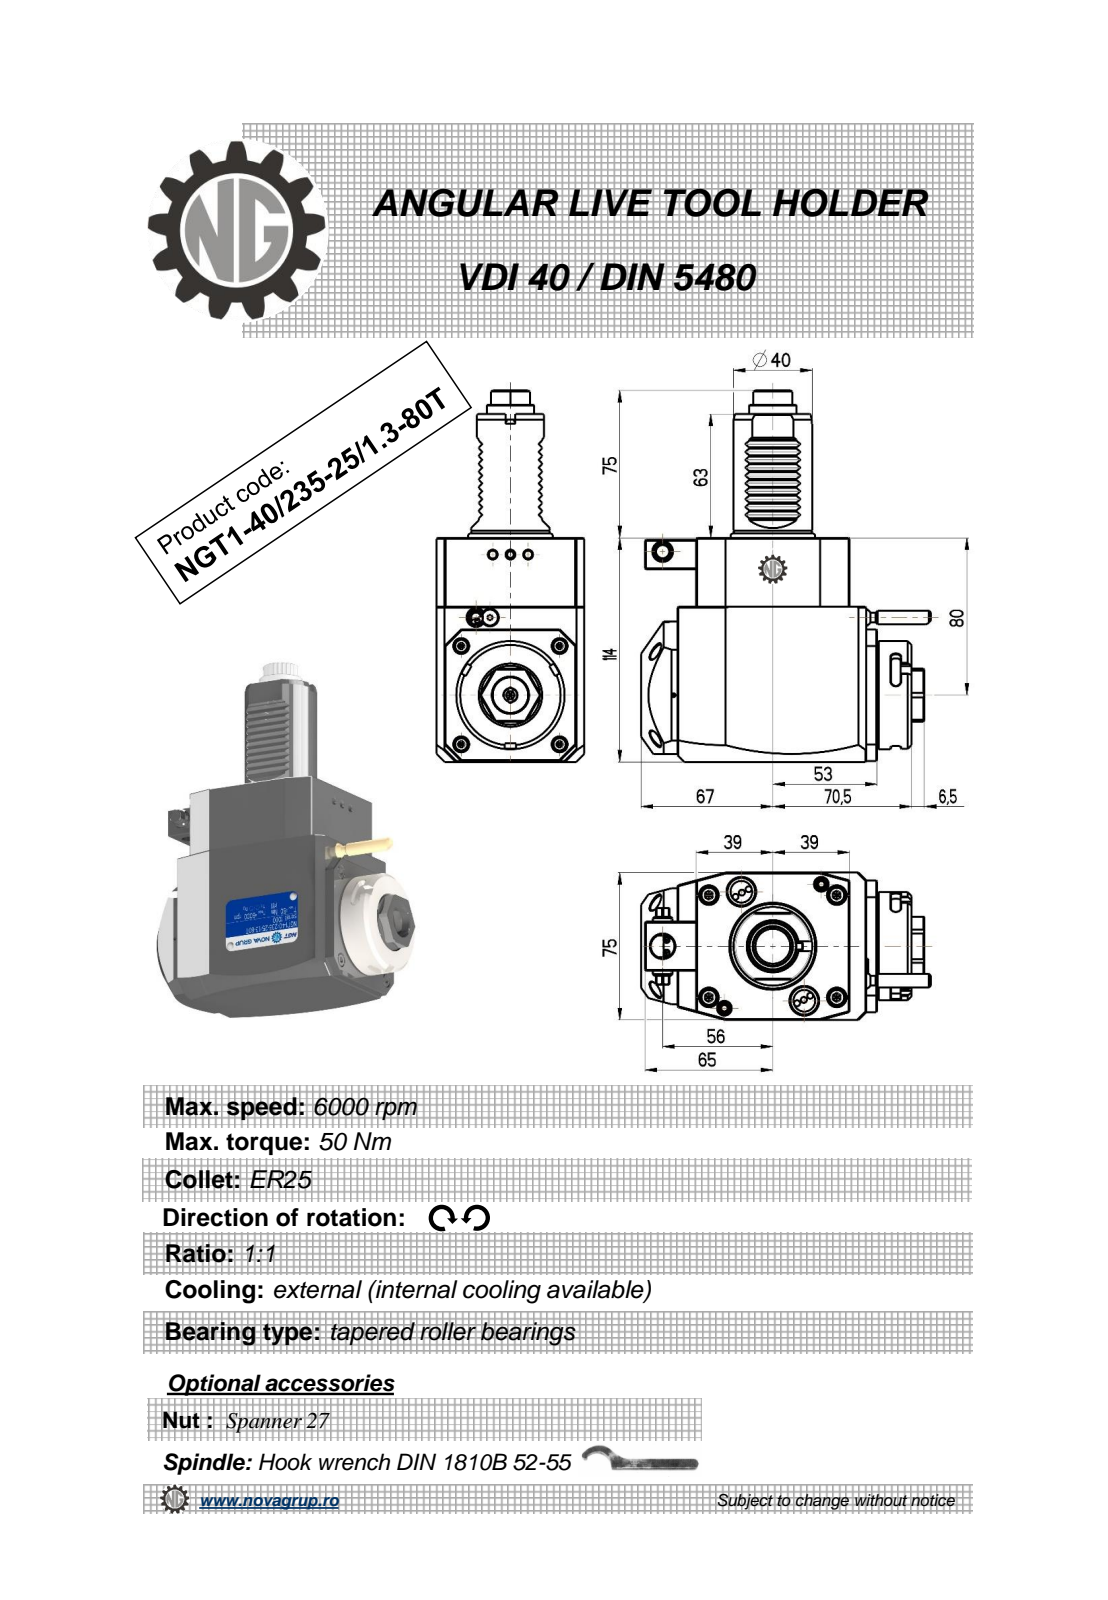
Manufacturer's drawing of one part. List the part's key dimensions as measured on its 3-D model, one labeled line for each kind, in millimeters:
Part name (STEP PRODUCT): NGT1_40_235_25_1_3_80T
STEP written by: PRO/ENGINEER BY PARAMETRIC TECHNOLOGY CORPORATION, 2010280 (CONFIG_CONTROL_DESIGN)
Units: millimetres
Bodies: 1 solid, 508 faces (222 planar, 188 cylindrical, 98 other)
Overall size (bounding box): 189 × 147.33 × 75
Volume: 955 538 mm³ · Surface area: 71 405 mm²
Round holes (diameter × count): ⌀2.5 ×1, ⌀3 ×1, ⌀9.5 ×1, ⌀12 ×1, ⌀18 ×1
Round bosses / shafts (diameter × count): ⌀8 ×2, ⌀55 ×1, ⌀48 ×1, ⌀40 ×1, ⌀24 ×1, ⌀10 ×1, ⌀7 ×1, ⌀5 ×1
Partial cylindrical surfaces — rounded edges, fillets, slot ends (radius × count): R2.08 ×48, R0.3 ×20, R2.5 ×6, R15 ×2, R180 ×2, R3.85 ×1, R4.25 ×1, R9.08 ×1
Main face-to-face distances: 75, 114, 14, 17.5, 109.5, 78, 92, 31.5, 79, 28
Hole centre spacings: 36.47, 43.2, 71.5
